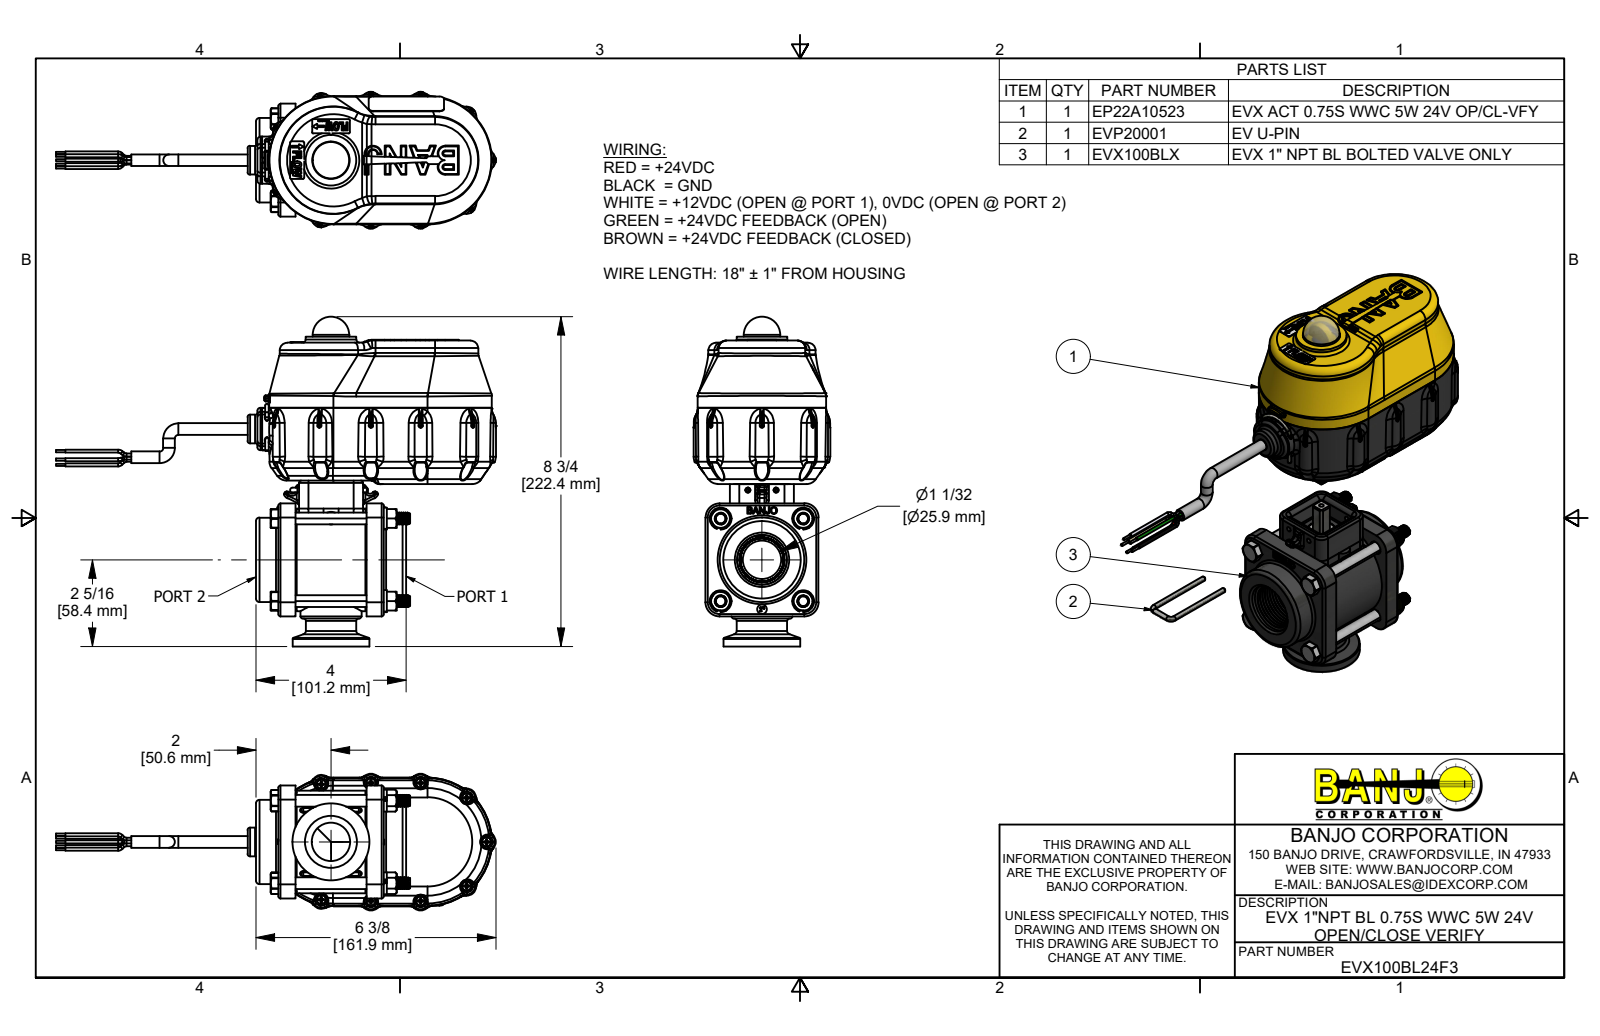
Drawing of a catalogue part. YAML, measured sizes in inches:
part_name: "EVX100BL24F3; EP22A10523; B61905PPHS; B632038PM (+8 more)"
step_written_by: "Autodesk Inventor 2021 (AUTOMOTIVE_DESIGN)"
units: inches
bodies: {solids: 98, faces: 12114, planar: 3282, cylindrical: 3513, other: 5319}
overall_size: [11.685, 8.757, 3.63]
volume: 52.56
surface_area: 598.7
round_holes:
  - {diameter: 0.095, count: 11}
  - {diameter: 0.15, count: 11}
  - {diameter: 0.08, count: 7}
  - {diameter: 0.107, count: 4}
  - {diameter: 0.126, count: 4}
  - {diameter: 0.136, count: 4}
  - {diameter: 0.148, count: 4}
  - {diameter: 0.15, count: 4}
  - {diameter: 0.17, count: 4}
  - {diameter: 0.252, count: 4}
  - {diameter: 0.322, count: 4}
  - {diameter: 0.135, count: 3}
round_bosses_or_shafts:
  - {diameter: 0.268, count: 60}
  - {diameter: 0.08, count: 25}
  - {diameter: 0.25, count: 17}
  - {diameter: 0.14, count: 11}
  - {diameter: 0.108, count: 11}
  - {diameter: 0.085, count: 11}
  - {diameter: 0.058, count: 10}
  - {diameter: 0.313, count: 5}
partial_cylinders:
  - {radius: 0.013, count: 180}
  - {radius: 0.04, count: 145}
  - {radius: 0.01, count: 84}
  - {radius: 0.02, count: 72}
  - {radius: 0.06, count: 58}
  - {radius: 0.005, count: 53}
  - {radius: 0.03, count: 38}
  - {radius: 0.08, count: 28}
face_to_face_distances: [0.1, 2.565, 0.055, 0.211, 0.06, 0.151, 0.46, 2.345, 0.125, 0.045]
hole_center_spacings: [1.55, 2.192, 2.656, 1.046, 1.513, 1.662, 1.891, 2.69]
